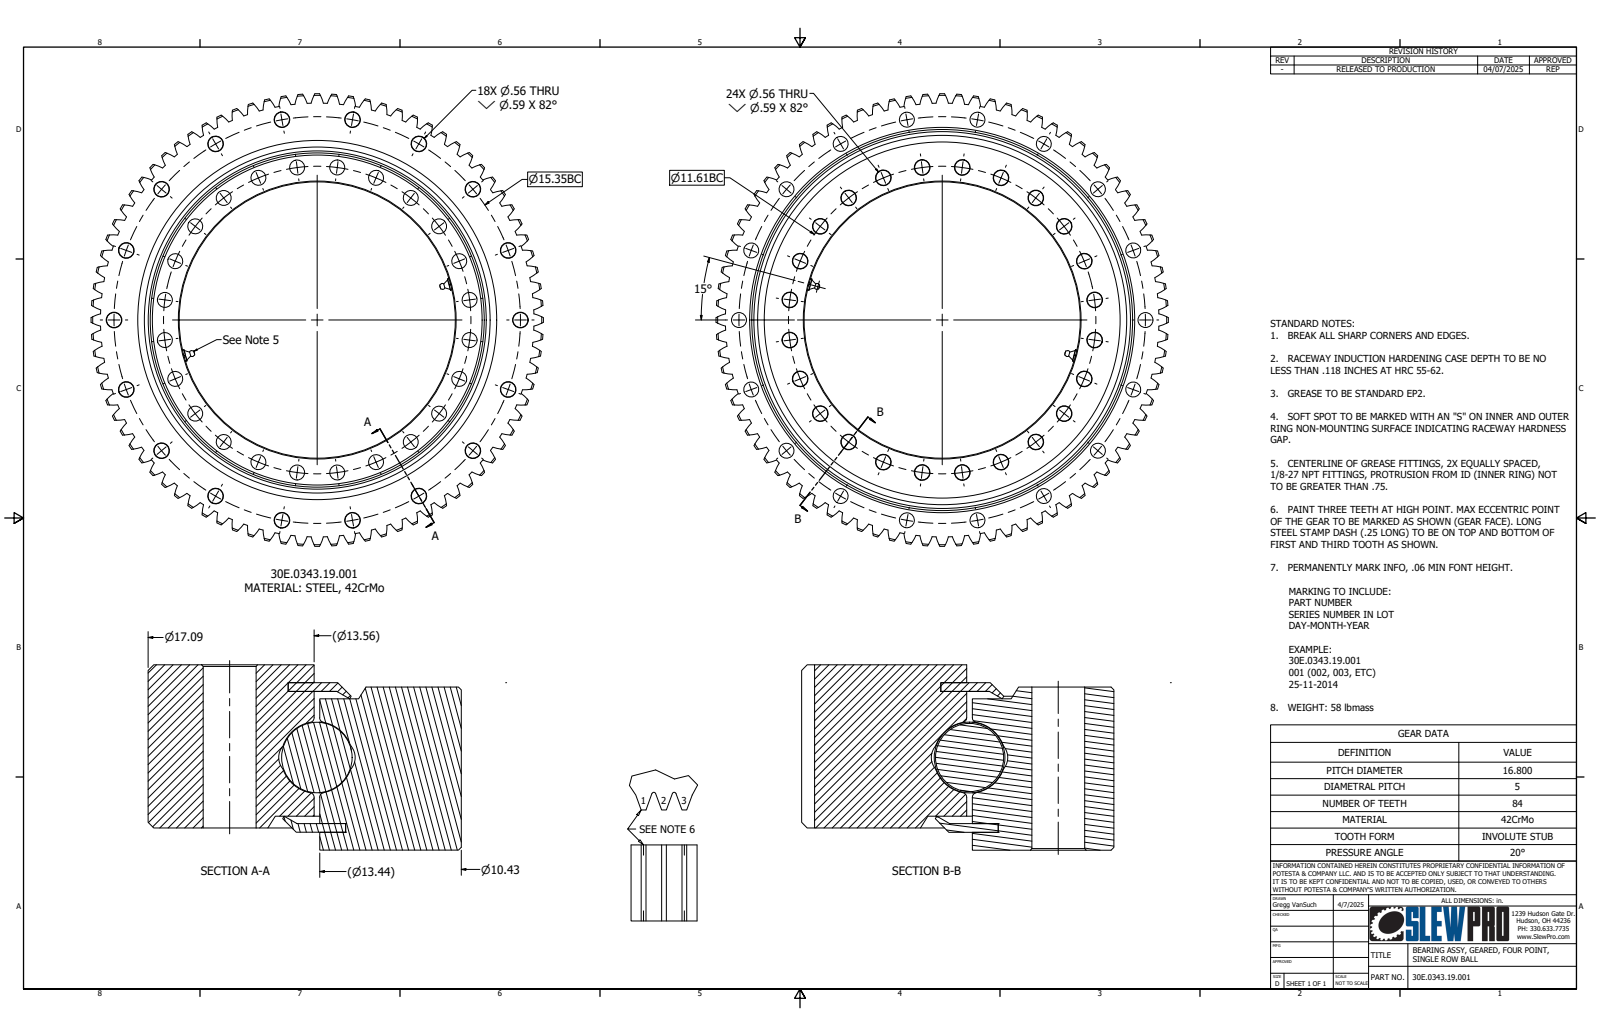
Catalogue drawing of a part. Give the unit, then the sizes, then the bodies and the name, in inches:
Units: inches
Overall size (bounding box): 17.086 × 17.086 × 1.968
Round holes (diameter × count): ⌀0.562 ×42, ⌀0.1 ×2, ⌀0.877 ×1, ⌀10.433 ×1, ⌀12.89 ×1, ⌀13.56 ×1, ⌀14.111 ×1
Round bosses / shafts (diameter × count): ⌀14.11 ×1, ⌀13.44 ×1, ⌀12.889 ×1, ⌀0.875 ×1
Partial cylindrical surfaces — rounded edges, fillets, slot ends (radius × count): R2.054 ×168, R8.19 ×1, R8.543 ×1
Main face-to-face distances: 1.496, 0.046, 1.732, 0.236, 1.968, 0.046, 0.093, 0.19, 1.778, 1.542
Hole centre spacings: 5.807, 9.214, 7.07, 11.515, 8.212, 10.058, 11.219, 1.516
Volume: 205.6 in³ · Surface area: 1 035 in²
Bodies: 7 solids, 819 faces (38 planar, 398 cylindrical, 383 other)
Part name (STEP PRODUCT): 30E.0343.19.001; Spur Gears1; 1_8 NPT Fitting
STEP written by: Autodesk Inventor 2026 (AUTOMOTIVE_DESIGN)
